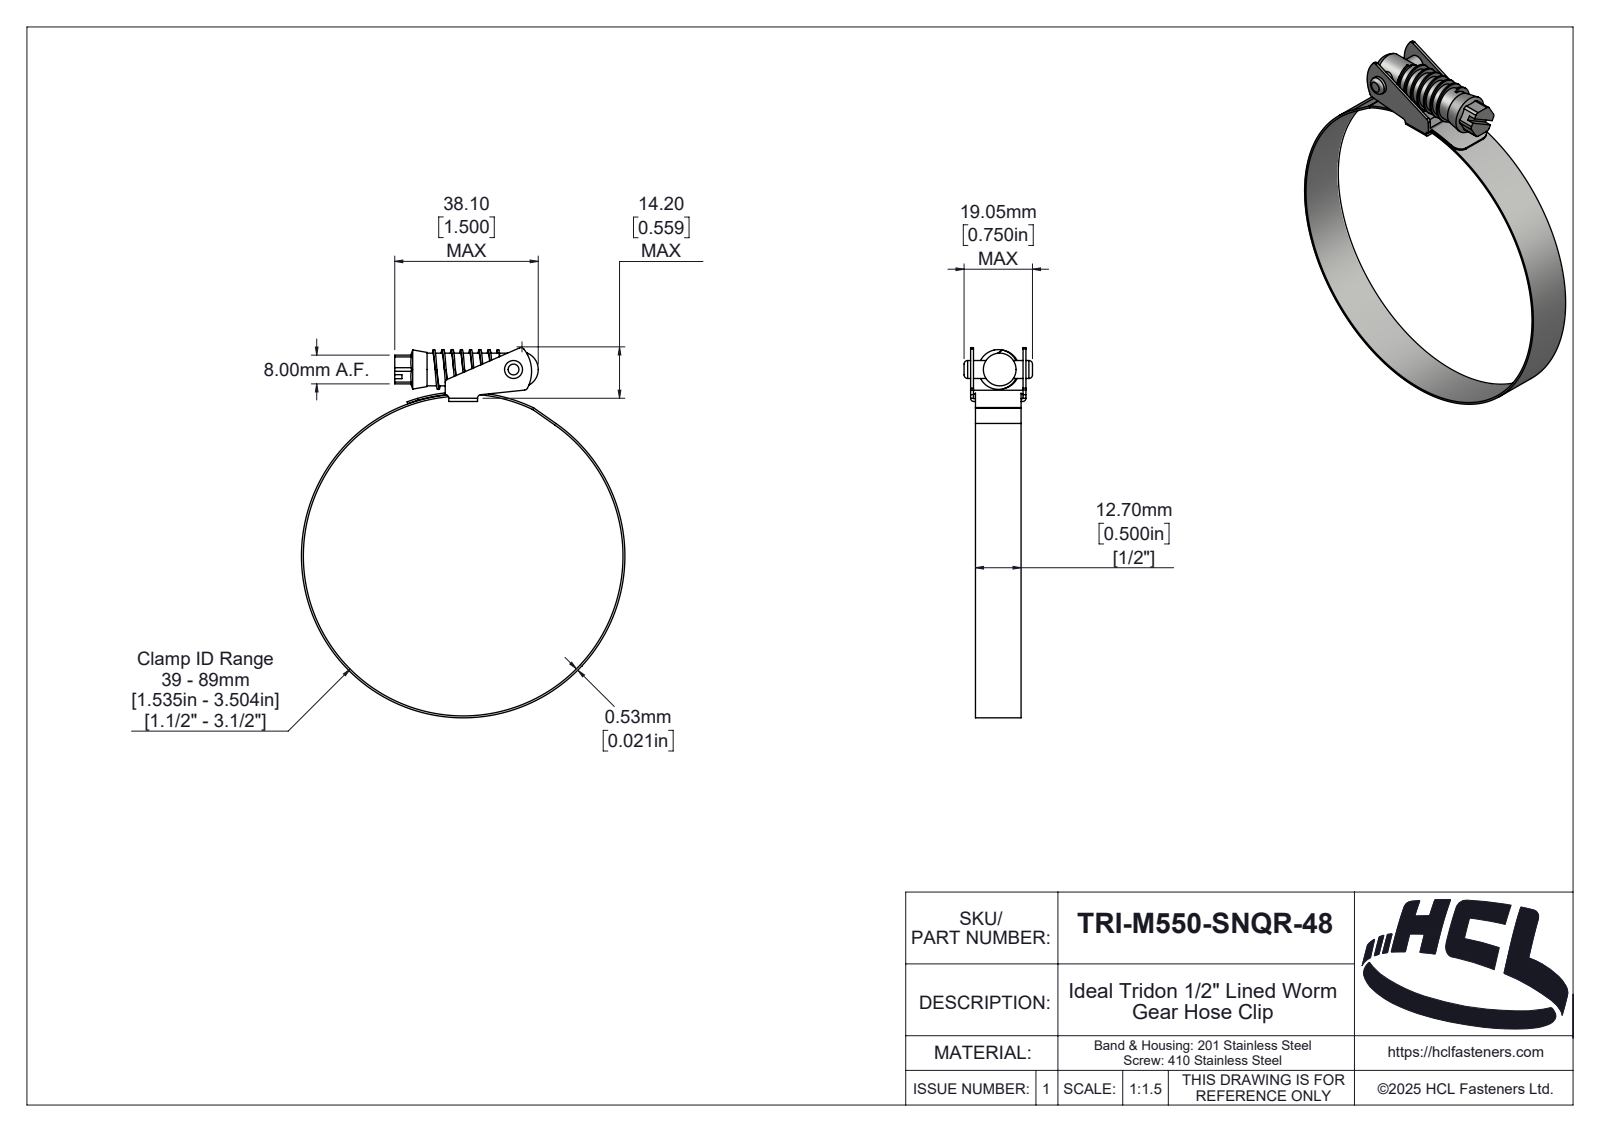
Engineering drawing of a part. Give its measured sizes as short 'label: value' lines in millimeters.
name: TRI-M550-SNQR-48
written by: SolidWorks 2025 (AUTOMOTIVE_DESIGN)
unit: mm
bodies: 5 solids, 222 faces (44 planar, 112 cylindrical, 66 other)
size: 103.02 × 90.06 × 19.05
volume: 5 180 mm³; area: 11 453 mm²
holes: 1× ⌀5, 1× ⌀89
bosses: 1× ⌀90.06, 1× ⌀9.1
rounds: 11× R1, 2× R0.1, 2× R0.9, 2× R3, 1× R0.46, 1× R1.89, 1× R2, 1× R2.35
face distances: 0.8, 14.6, 1.35, 14.05, 0.55, 13.25, 15.4, 13.8, 12.7, 1
hole spacings: 53.76
